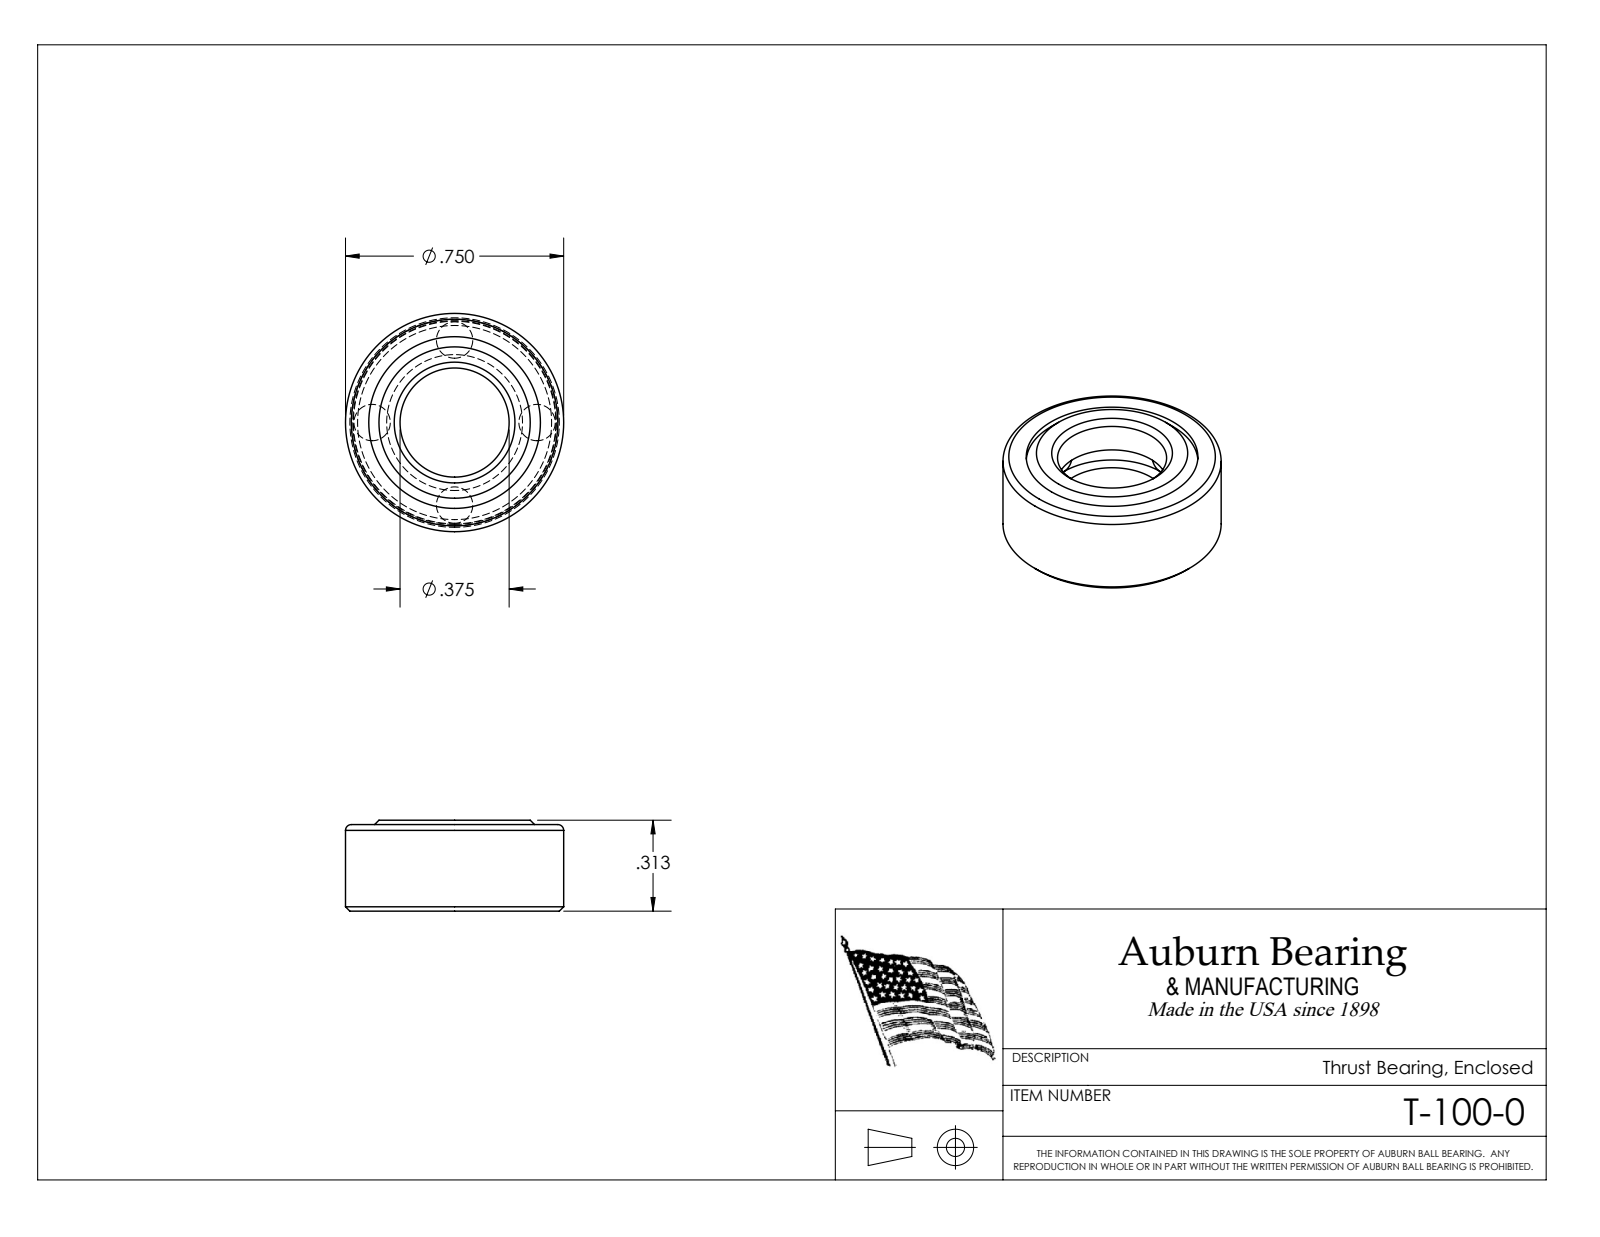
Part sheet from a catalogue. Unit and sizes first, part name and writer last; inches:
Units: inches
Overall size (bounding box): 0.75 × 0.75 × 0.313
Round holes (diameter × count): ⌀0.375 ×1, ⌀0.59 ×1, ⌀0.71 ×1
Round bosses / shafts (diameter × count): ⌀0.75 ×1, ⌀0.696 ×1
Main face-to-face distances: 0.119, 0.194, 0.278, 0.298, 0.02, 0.159, 0.179, 0.075, 0.084, 0.104
Volume: 0.071 in³ · Surface area: 3.157 in²
Bodies: 6 solids, 28 faces (9 planar, 7 cylindrical, 12 other)
Part name (STEP PRODUCT): T-100-0
STEP written by: SolidWorks 2016 (CONFIG_CONTROL_DESIGN)
